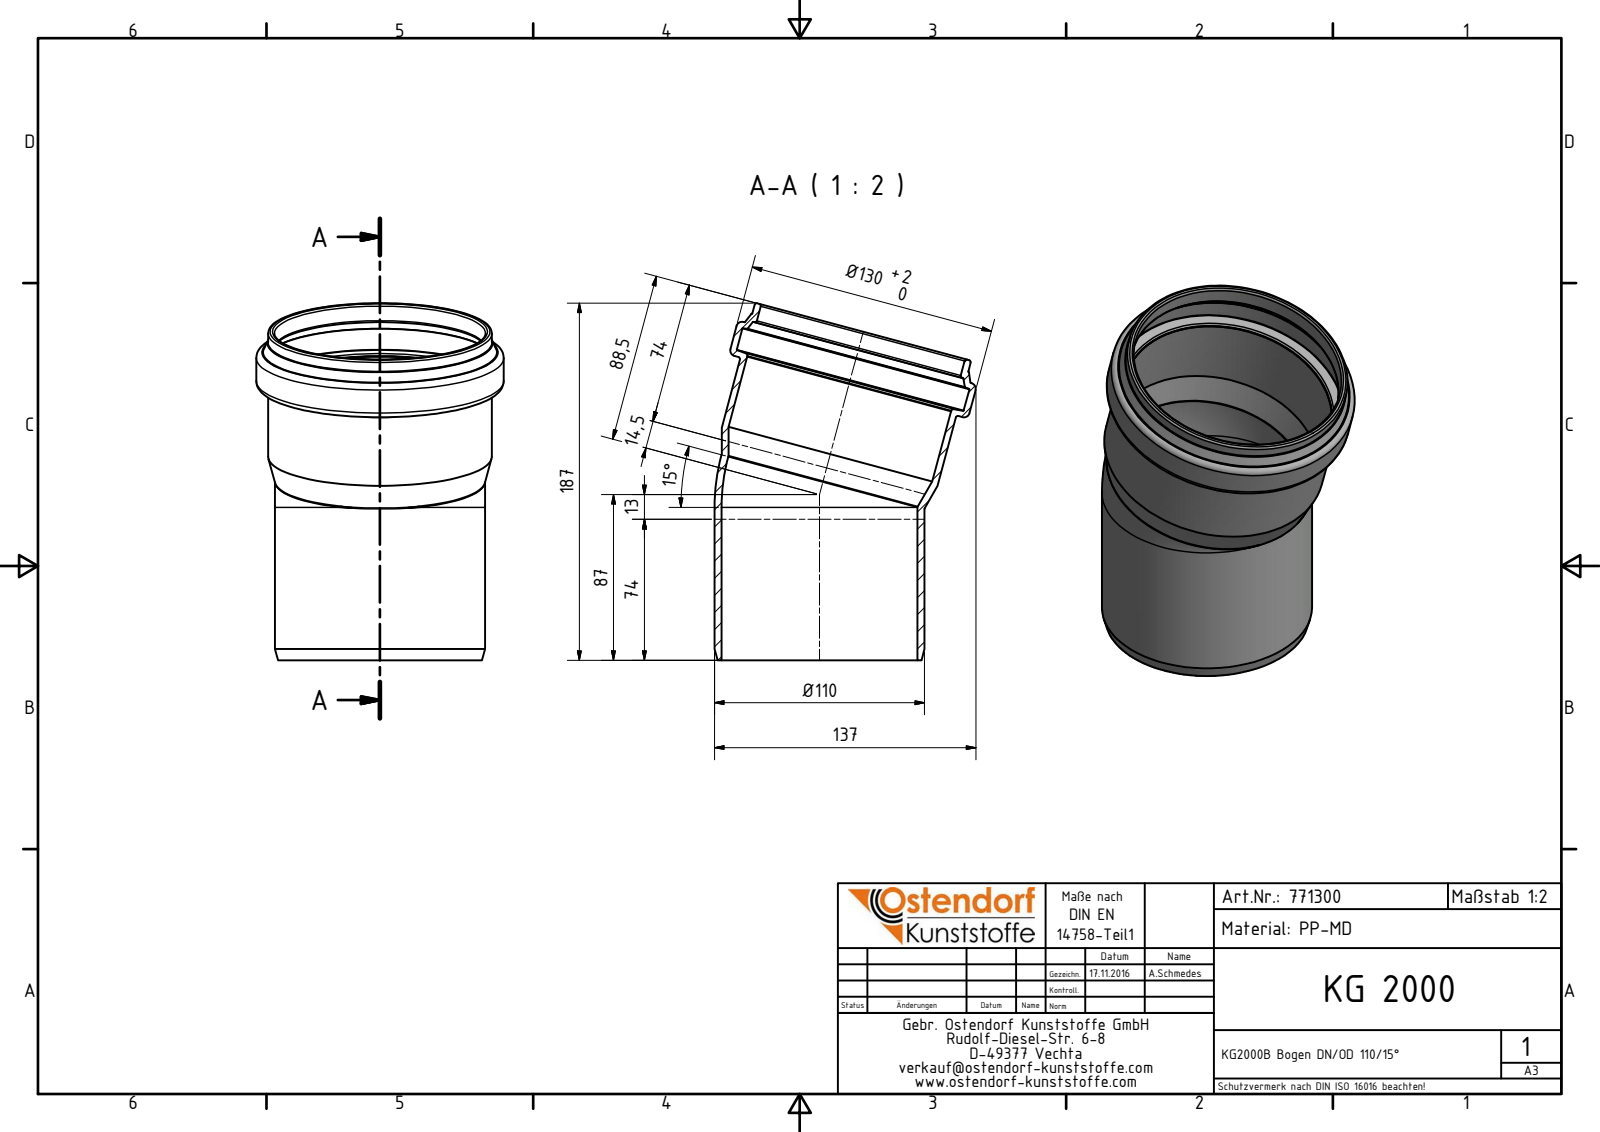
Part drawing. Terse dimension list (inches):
name: 771300 KG2000B Bogen DN_OD 110_15°
written by: Autodesk Inventor 2016 (AUTOMOTIVE_DESIGN)
unit: in
bodies: 1 solid, 43 faces (5 planar, 11 cylindrical, 27 other)
size: 7.381 × 5.403 × 5.118
volume: 13.7 in³; area: 202.4 in²
holes: 2× ⌀4.051, 1× ⌀4.362, 1× ⌀4.366, 1× ⌀4.858
bosses: 2× ⌀4.343, 1× ⌀5.118, 1× ⌀4.626, 1× ⌀4.622
face distances: 1.173, 0.728, 0.445, 0.057, 0.672, 1.117
